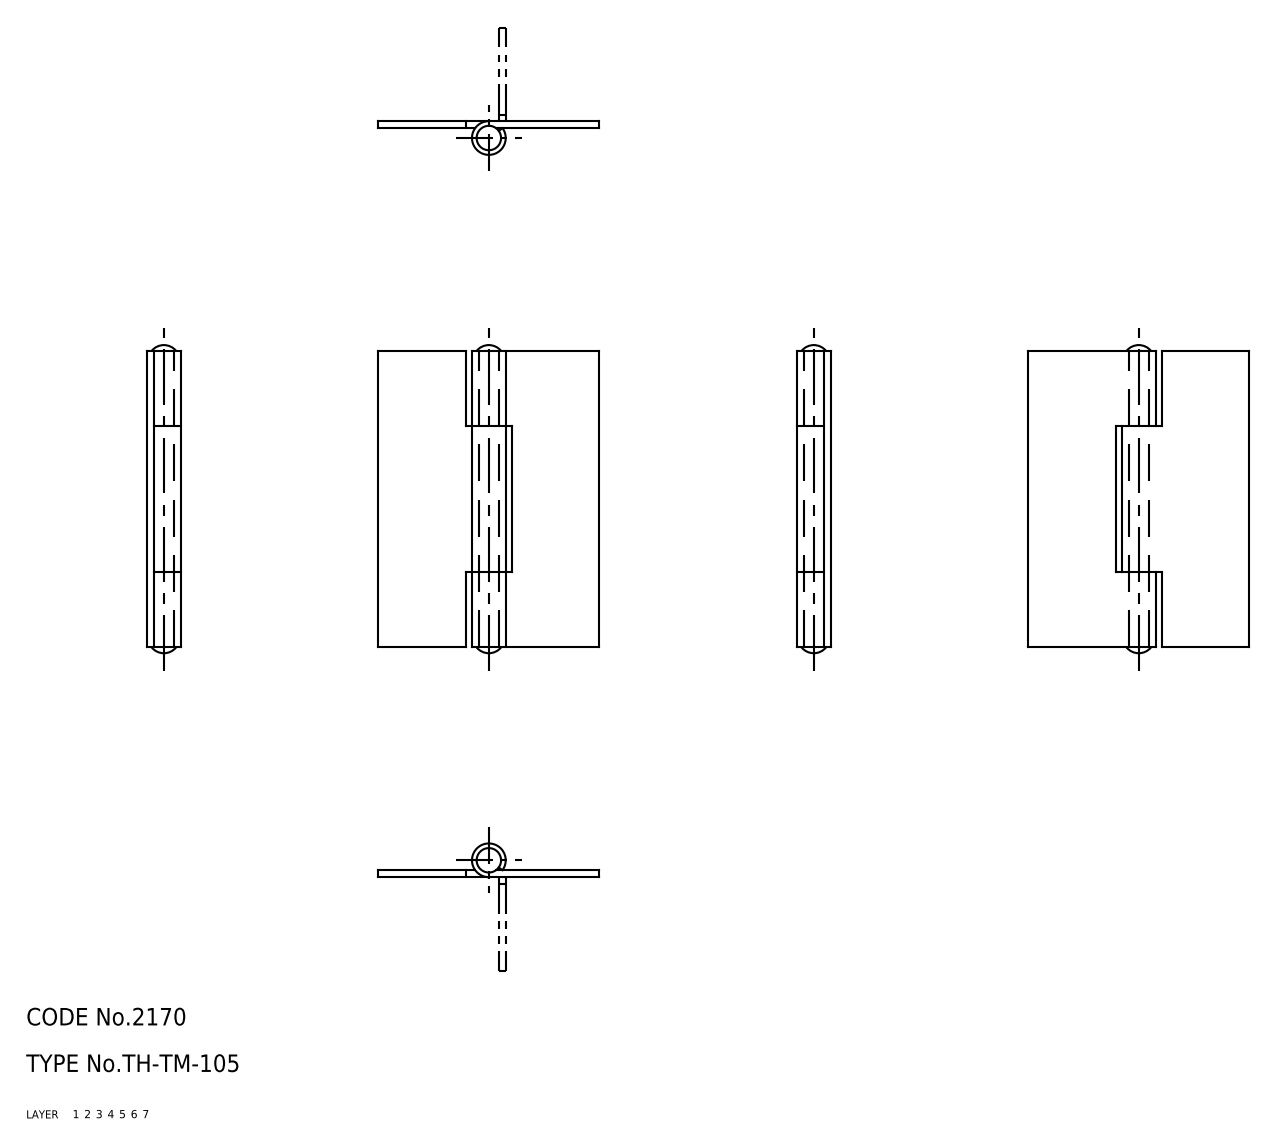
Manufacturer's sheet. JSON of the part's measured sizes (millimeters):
{"part_name": "67110369; 67110382; 67110395", "step_written_by": "CADfix (AUTOMOTIVE_DESIGN)", "units": "millimeters", "bodies": {"solids": 3, "faces": 32, "planar": 0, "cylindrical": 0, "other": 32}, "overall_size": [53, 38, 5.8], "volume_mm3": 3308, "surface_area_mm2": 5738}
